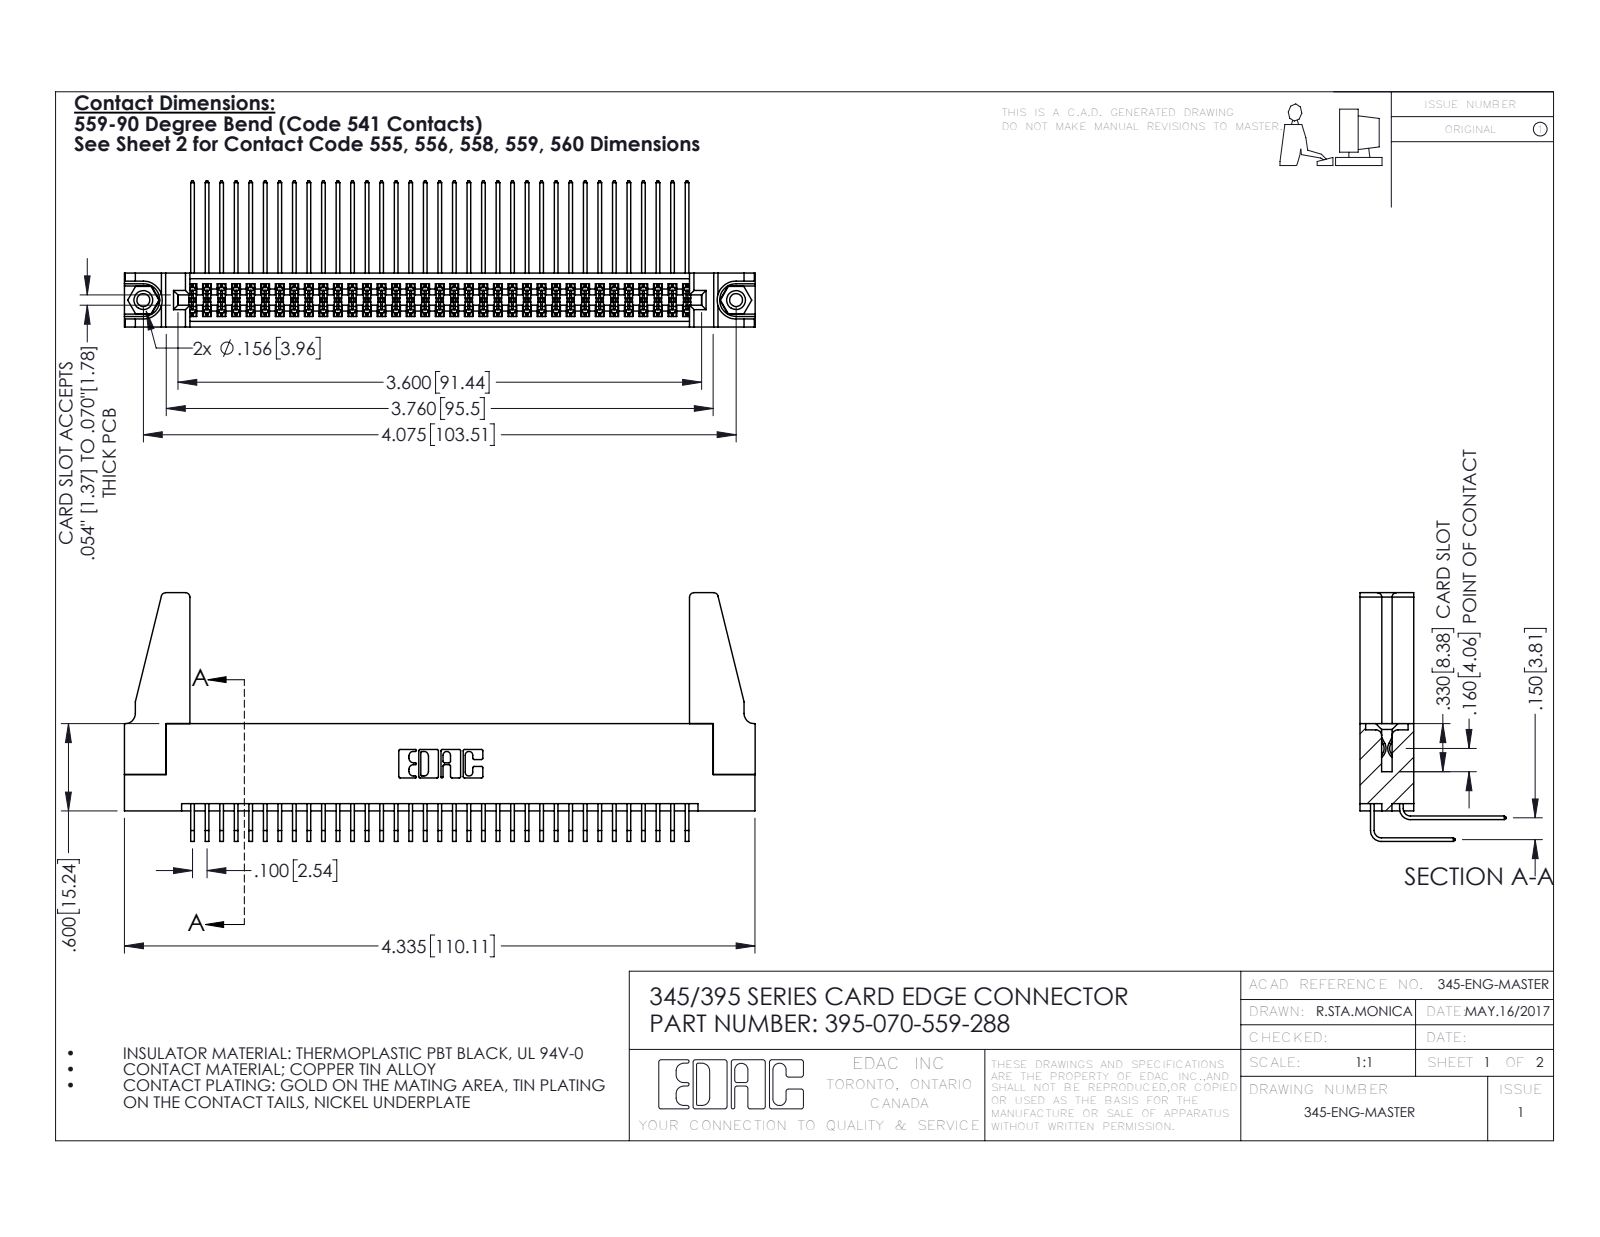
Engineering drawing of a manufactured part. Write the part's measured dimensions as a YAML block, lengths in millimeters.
part_name: "345-220-078_345-220-088; 395-070-559-288; 345 Part_Flush Mounting Lugs - 0.156 Dia-TH; 345-250-001_345-250-001-102 (+2 more)"
step_written_by: "SolidWorks 2016 (CONFIG_CONTROL_DESIGN)"
units: millimeters
bodies: {solids: 75, faces: 3890, planar: 2602, cylindrical: 1272, other: 16}
overall_size: [110.1, 43.4, 25.5]
volume: 14300
surface_area: 21200
round_holes:
  - {diameter: 2.3, count: 2}
  - {diameter: 3.2, count: 2}
  - {diameter: 4, count: 2}
  - {diameter: 1.6, count: 1}
round_bosses_or_shafts:
  - {diameter: 3.9, count: 2}
partial_cylinders:
  - {radius: 0.2, count: 105}
  - {radius: 0.3, count: 22}
  - {radius: 0.8, count: 8}
  - {radius: 0.2, count: 6}
  - {radius: 0.8, count: 6}
  - {radius: 0.7, count: 3}
  - {radius: 0.4, count: 2}
  - {radius: 0.5, count: 2}
face_to_face_distances: [1.8, 7.6, 9.4, 5.1, 2.5, 6.9, 0.6, 5.7, 4.4, 3.8]
hole_center_spacings: [6.9, 97.5, 103.5]
